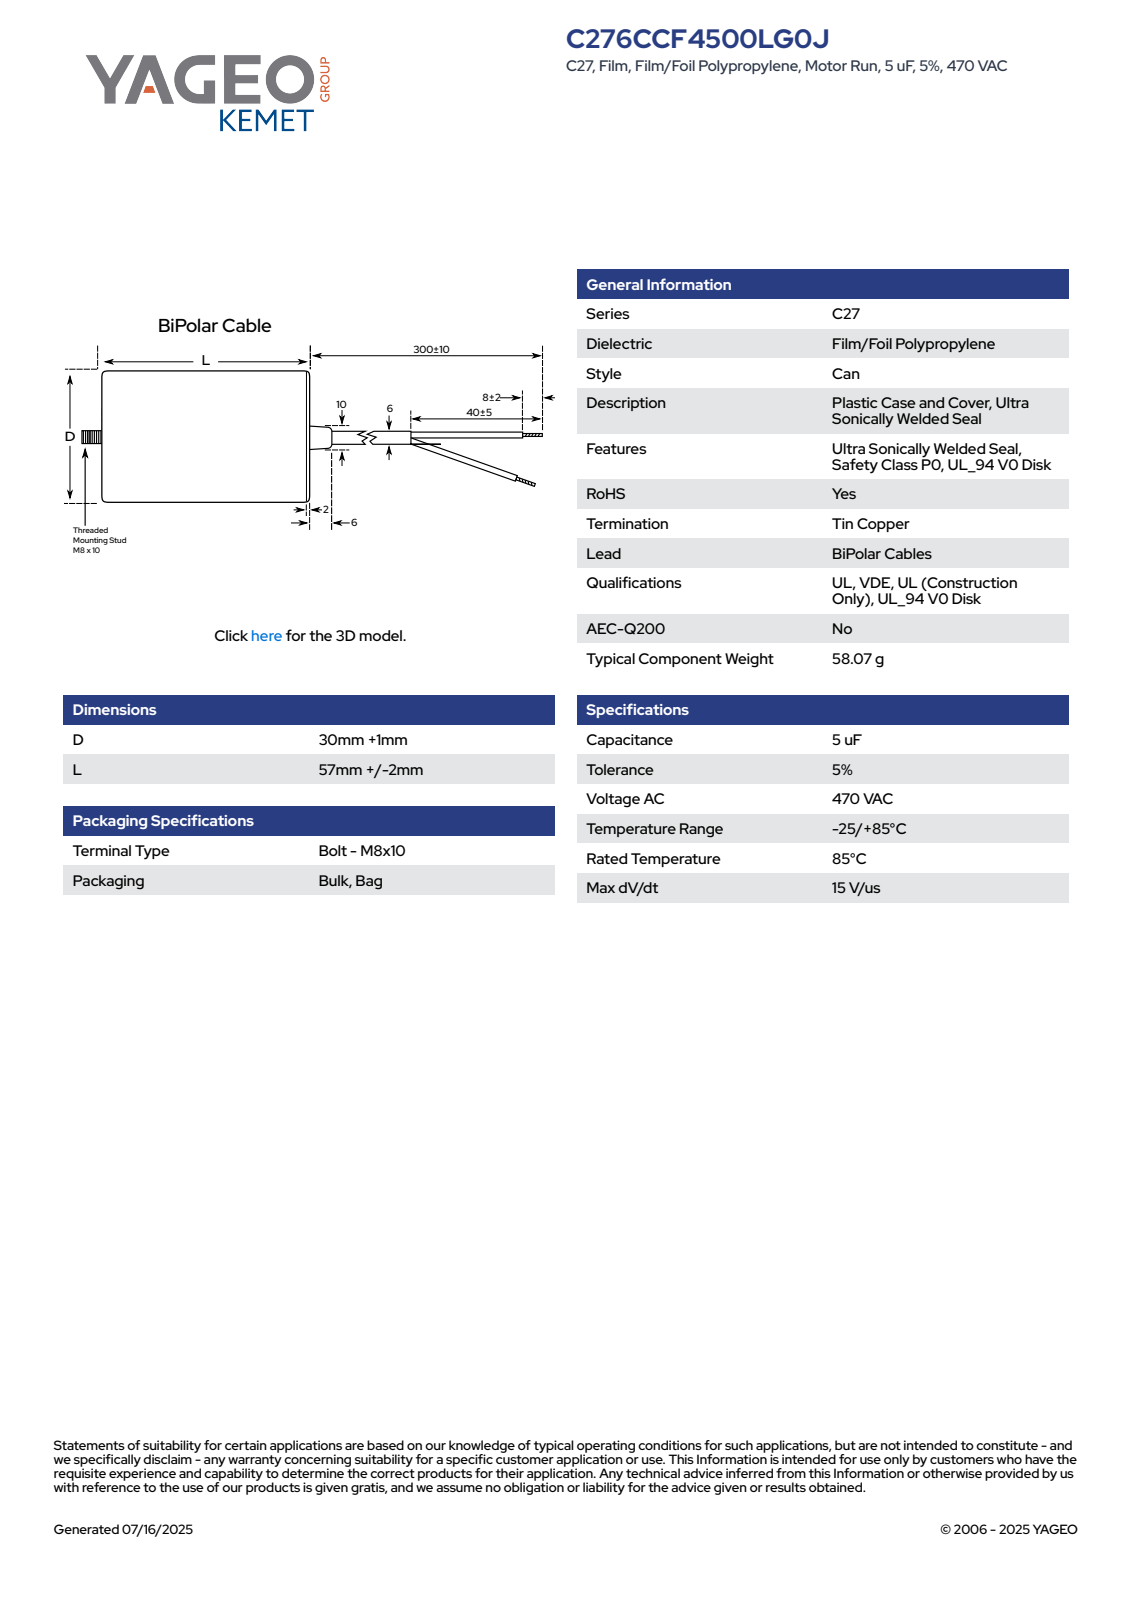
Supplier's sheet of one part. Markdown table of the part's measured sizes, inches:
| quantity | value |
| --- | --- |
| part name | CFM_KC27BI_30X57_D31L59 |
| STEP written by | SolidWorks 2014 (AUTOMOTIVE_DESIGN) |
| units | inches |
| bodies | 2 solids, 82 faces (28 planar, 15 cylindrical, 39 other) |
| overall size | 2.953 × 1.221 × 1.22 |
| volume | 2.699 in³ |
| surface area | 12.22 in² |
| round holes (diameter × count) | 1.063 × 1 |
| round bosses / shafts (diameter × count) | 1.22 × 1, 0.315 × 1 |
| partial cylindrical surfaces (radius × count) | 0.611 × 1 |
| main face-to-face distances | 2.244, 2.323, 0.079, 0.394, 2.638, 2.717, 2.953, 2.559, 0.315, 0.236 |
